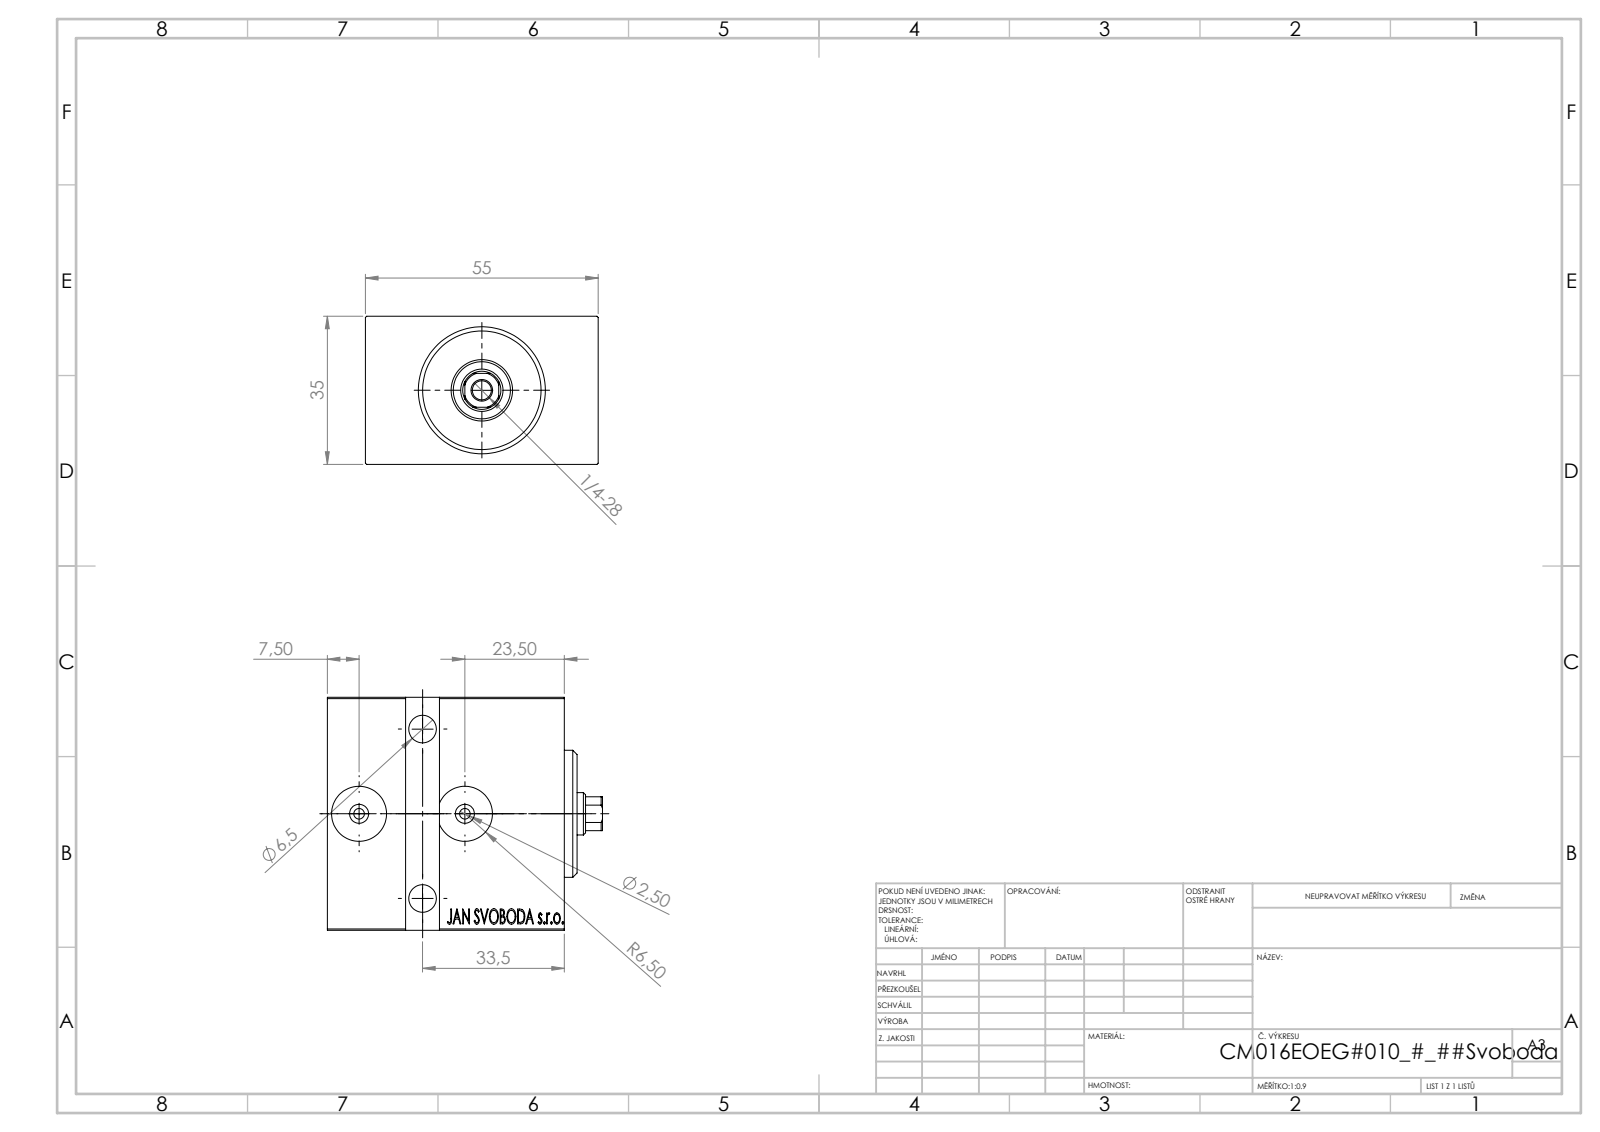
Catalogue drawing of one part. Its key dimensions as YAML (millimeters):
part_name: "V450CM_E_VCP; V450CM_VC_B; V450CM_E_Body"
step_written_by: "SolidWorks 2019 (CONFIG_CONTROL_DESIGN)"
units: millimeters
bodies: {solids: 3, faces: 852, planar: 411, cylindrical: 47, other: 394}
overall_size: [65, 55, 35]
volume: 105743
surface_area: 24598
round_holes:
  - {diameter: 2.5, count: 2}
  - {diameter: 6.5, count: 2}
  - {diameter: 10.5, count: 2}
  - {diameter: 13, count: 2}
  - {diameter: 4.5, count: 1}
  - {diameter: 10, count: 1}
  - {diameter: 13.5, count: 1}
  - {diameter: 14.5, count: 1}
  - {diameter: 16, count: 1}
  - {diameter: 25, count: 1}
round_bosses_or_shafts:
  - {diameter: 4.5, count: 2}
  - {diameter: 30, count: 1}
  - {diameter: 18, count: 1}
partial_cylinders:
  - {radius: 4.5, count: 1}
face_to_face_distances: [35, 55, 56, 5, 51, 8, 3, 1, 59, 46]
hole_center_spacings: [25, 22.36, 40]
